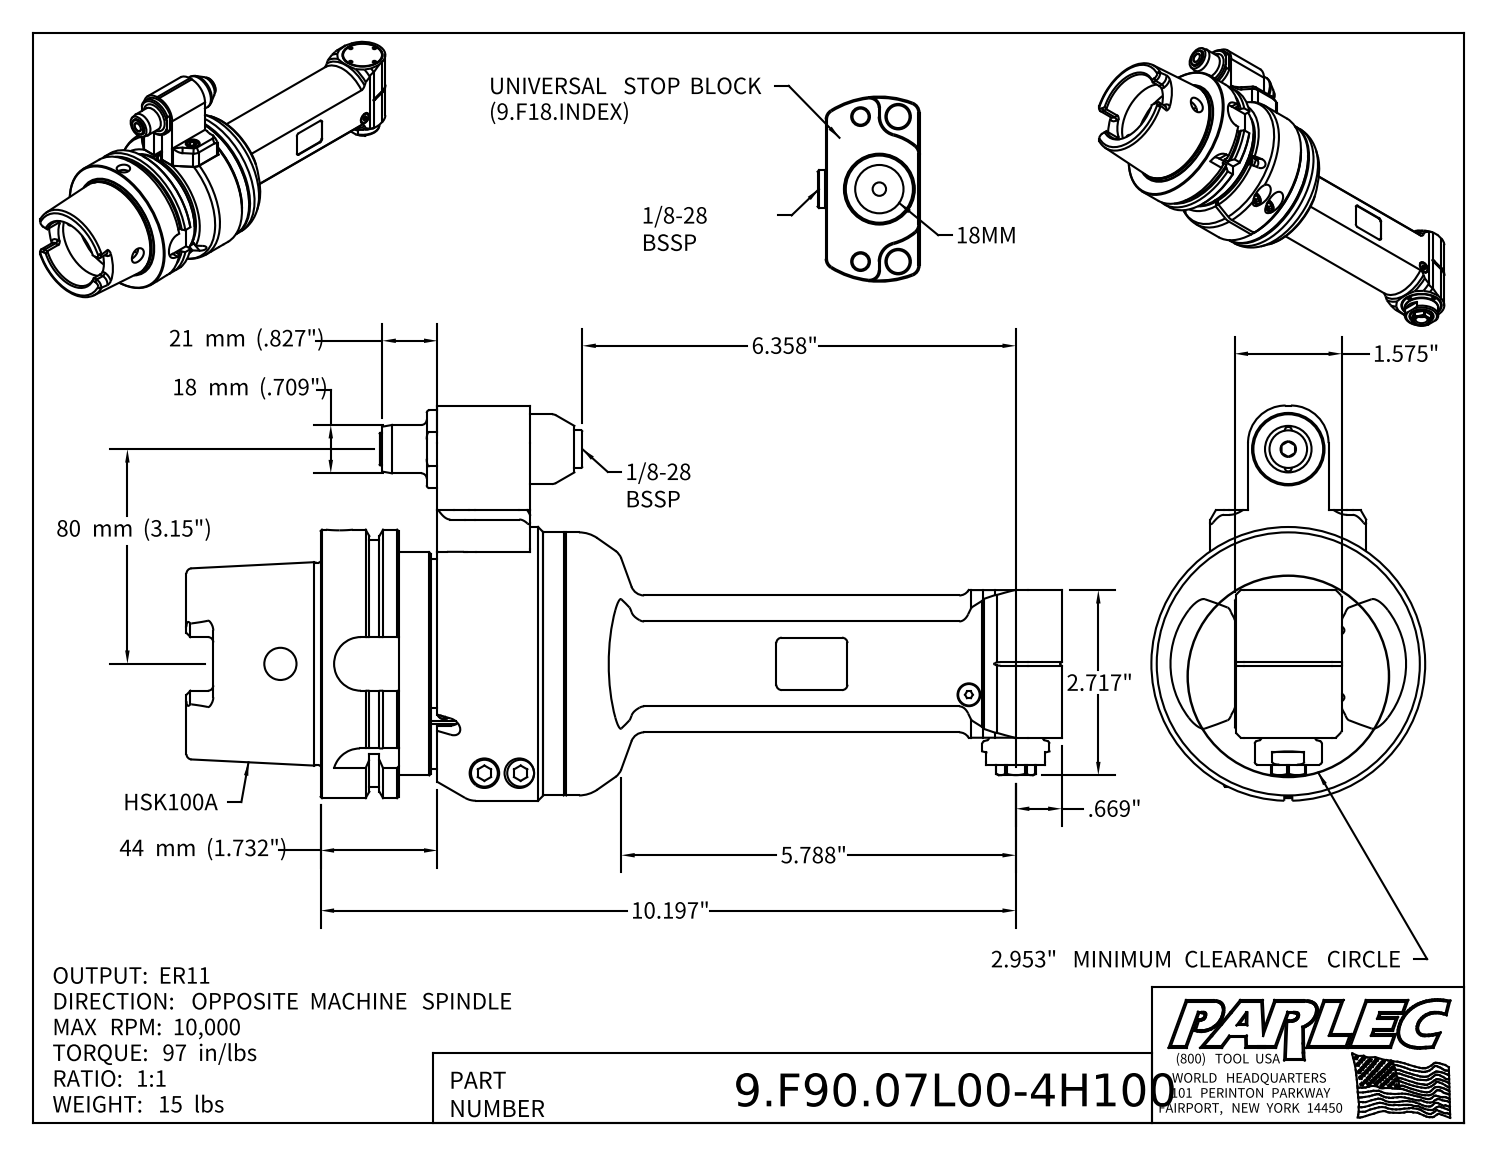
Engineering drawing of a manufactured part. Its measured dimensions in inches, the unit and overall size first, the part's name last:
Units: inches
Overall size (bounding box): 12.835 × 5.796 × 4.016
Round holes (diameter × count): ⌀0.102 ×6, ⌀0.197 ×4, ⌀0.409 ×2, ⌀0.433 ×2, ⌀0.472 ×2, ⌀0.098 ×1, ⌀0.118 ×1, ⌀0.256 ×1, ⌀0.276 ×1, ⌀0.295 ×1, ⌀0.335 ×1, ⌀0.354 ×1
Round bosses / shafts (diameter × count): ⌀0.394 ×4, ⌀0.236 ×4, ⌀0.709 ×3, ⌀0.315 ×2, ⌀0.098 ×2, ⌀4.016 ×1, ⌀3.937 ×1, ⌀3.858 ×1
Partial cylindrical surfaces — rounded edges, fillets, slot ends (radius × count): R0.079 ×18, R0.157 ×5, R0.192 ×4, R0.394 ×4, R0.016 ×2, R0.02 ×2, R0.039 ×2, R0.138 ×2
Main face-to-face distances: 1.26, 1.575, 1.555, 0.197, 1.22, 0.65, 1.142, 3.268, 2.008, 1.929
Hole centre spacings: 0.492, 0.696, 0.276, 0.984, 9.933, 0.014, 0.478, 0.506
Volume: 73.53 in³ · Surface area: 260.1 in²
Bodies: 5 solids, 532 faces (249 planar, 138 cylindrical, 145 other)
Part name (STEP PRODUCT): 9.F90.07L00-4H100; 9_GA1_518_2 (Type 1, H100A, 80mm); 9FL1ATC; 9F18T180_ASM (+4 more)
STEP written by: Autodesk Inventor 2025 (AUTOMOTIVE_DESIGN)
